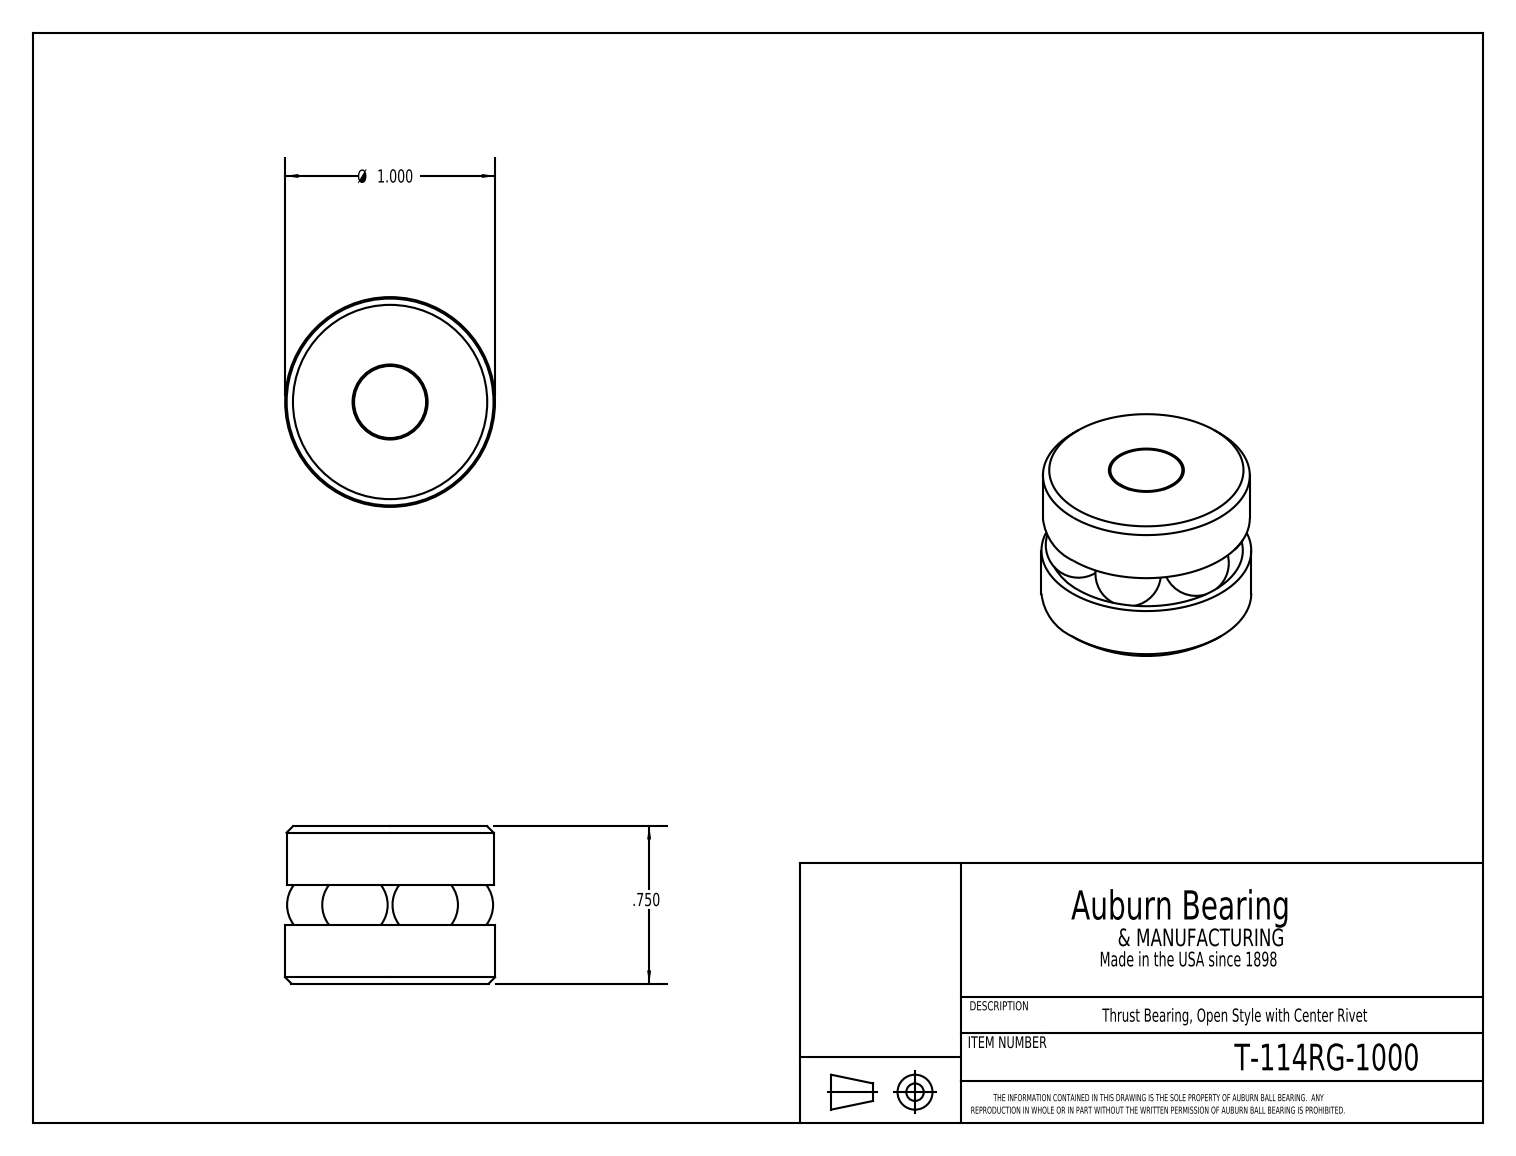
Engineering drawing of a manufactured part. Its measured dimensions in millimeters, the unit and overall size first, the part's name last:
Units: millimetres
Overall size (bounding box): 25.4 × 25.4 × 19.1
Round holes (diameter × count): ⌀4.2 ×1
Round bosses / shafts (diameter × count): ⌀25.4 ×1, ⌀25 ×1, ⌀4 ×1
Main face-to-face distances: 19.1, 7.1, 11.9, 4.7
Volume: 7 930 mm³ · Surface area: 4 894 mm²
Bodies: 9 solids, 27 faces (8 planar, 5 cylindrical, 14 other)
Part name (STEP PRODUCT): T-114RG_T-114RG-1000
STEP written by: SolidWorks 2016 (CONFIG_CONTROL_DESIGN)
